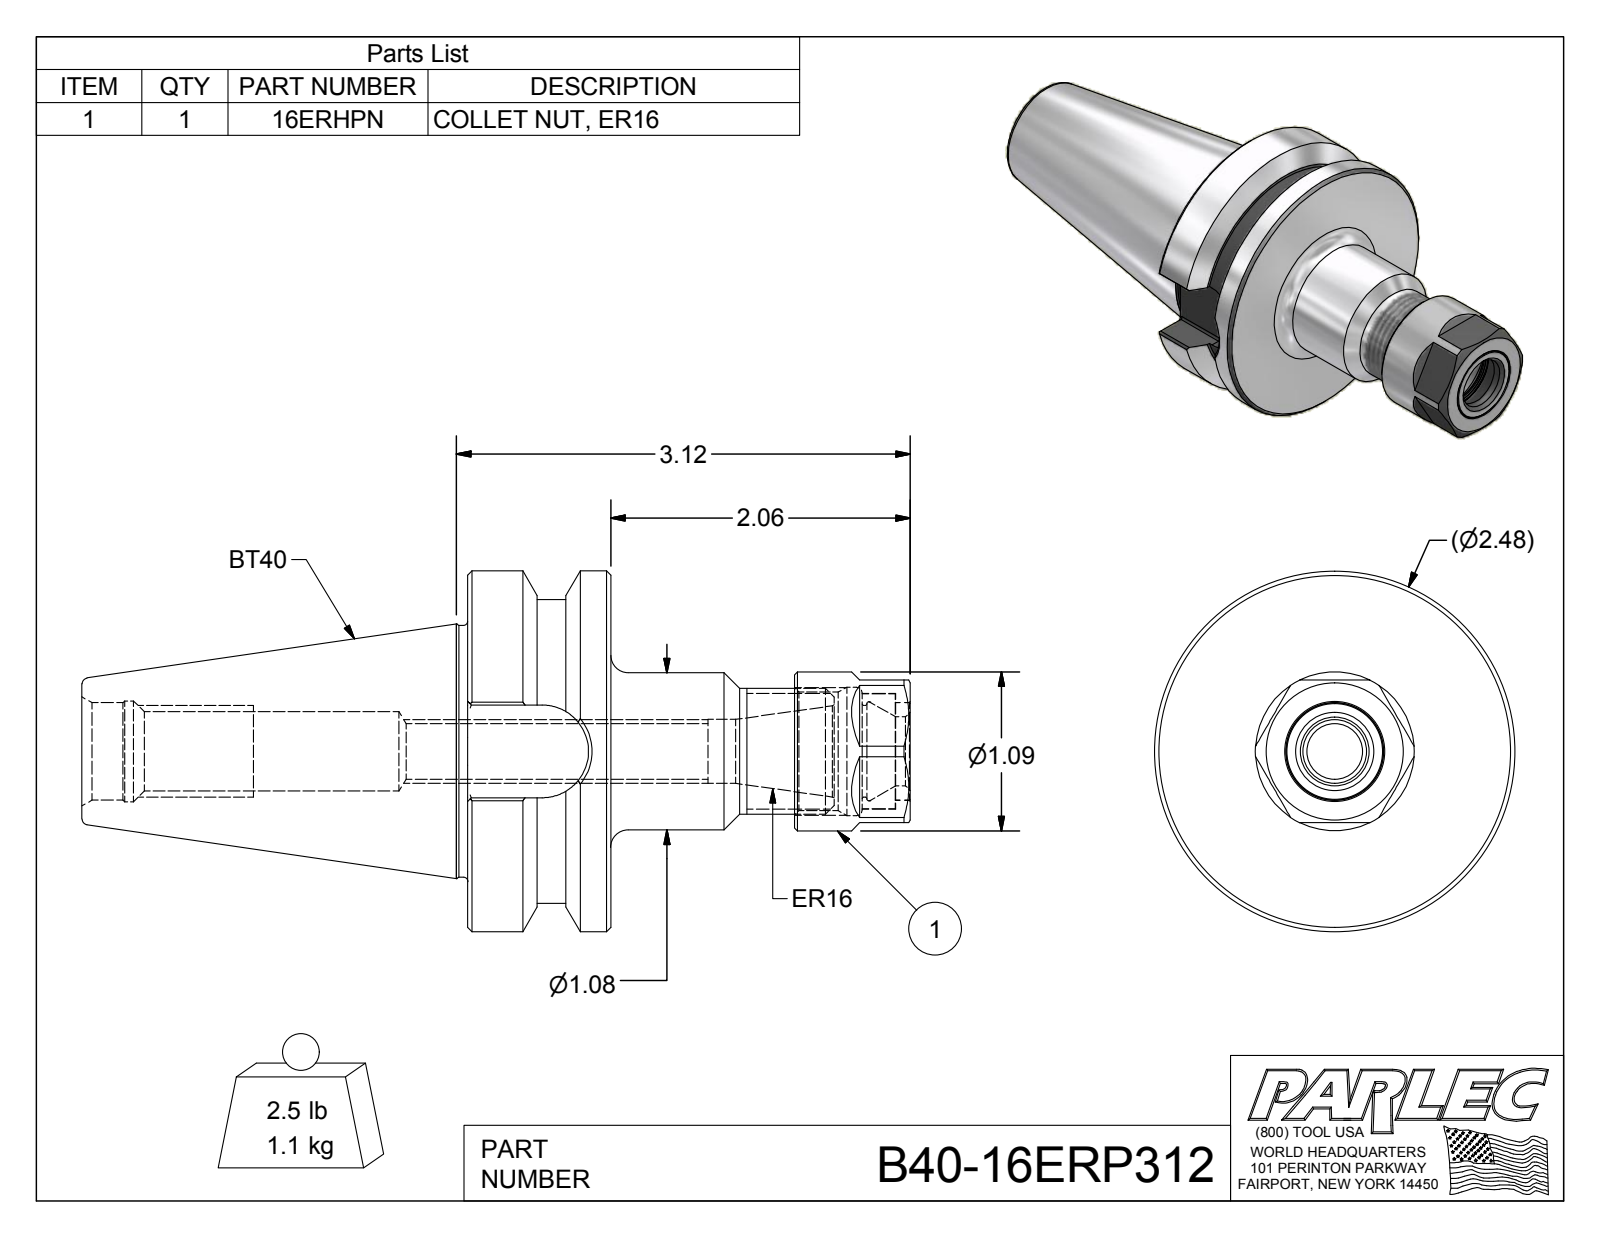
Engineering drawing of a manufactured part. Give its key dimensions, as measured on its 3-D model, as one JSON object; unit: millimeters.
{"part_name": "B40-16ERP312; B40-16ER3-1; 16ERHPN", "step_written_by": "Autodesk Inventor 2012 (AUTOMOTIVE_DESIGN)", "units": "millimeters", "bodies": {"solids": 3, "faces": 114, "planar": 44, "cylindrical": 33, "other": 37}, "overall_size": [144.7, 63, 63], "volume_mm3": 143200, "surface_area_mm2": 30920, "round_holes": [[9.7, 1], [11.2, 1], [12, 1], [13.8, 1], [16, 1], [17, 1], [17.1, 1], [17.3, 1], [17.6, 1], [20.2, 1], [20.7, 1], [22.4, 1]], "round_bosses_or_shafts": [[63, 1], [53, 1], [43.9, 1], [27.7, 1], [27.4, 1], [22, 1], [20.1, 1], [17, 1]], "partial_cylinders_radius": [[0.5, 8], [8.1, 1]], "face_to_face_distances": [25, 24.9, 45.2, 77.3, 52.3, 4.4, 20.5, 57, 32.1, 20.2]}
